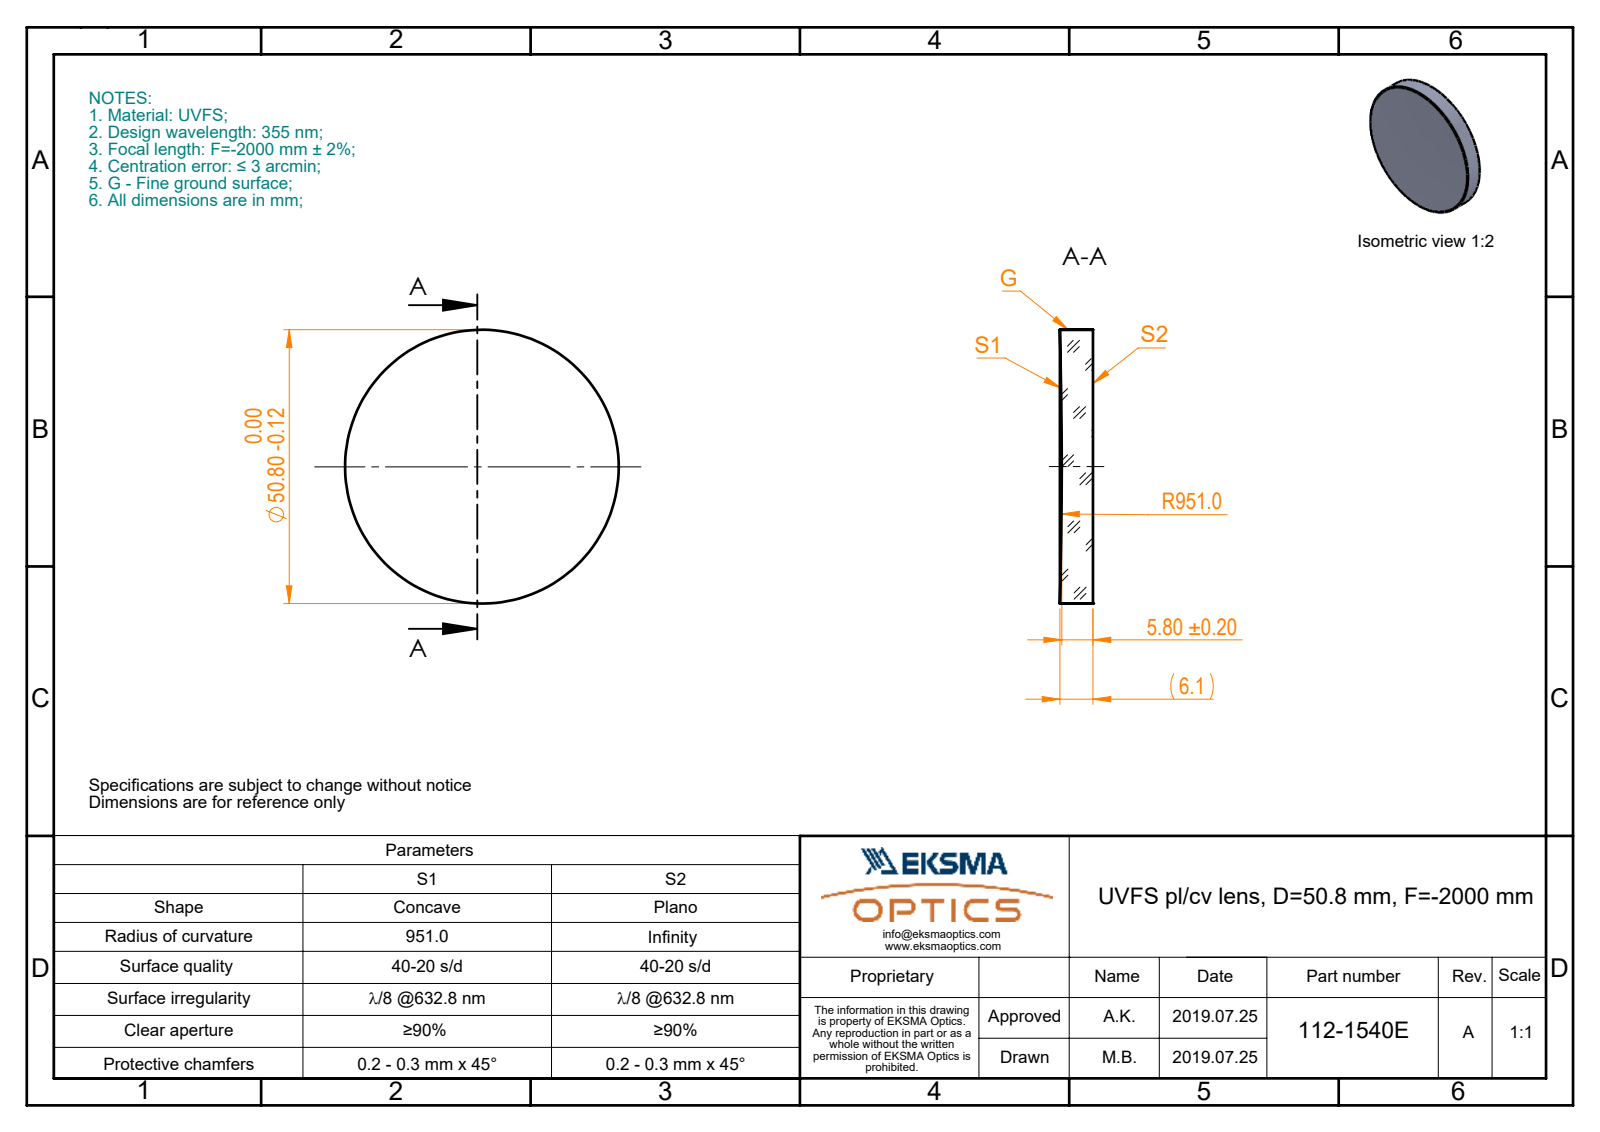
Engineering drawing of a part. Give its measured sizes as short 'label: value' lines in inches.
name: 112-1540E UVFS pl-cv 50.8 F-2000
written by: SolidWorks 2017 (CONFIG_CONTROL_DESIGN)
unit: in
bodies: 1 solid, 5 faces (1 planar, 2 cylindrical, 2 other)
size: 2 × 2 × 0.242
volume: 0.738 in³; area: 7.803 in²
bosses: 1× ⌀2
